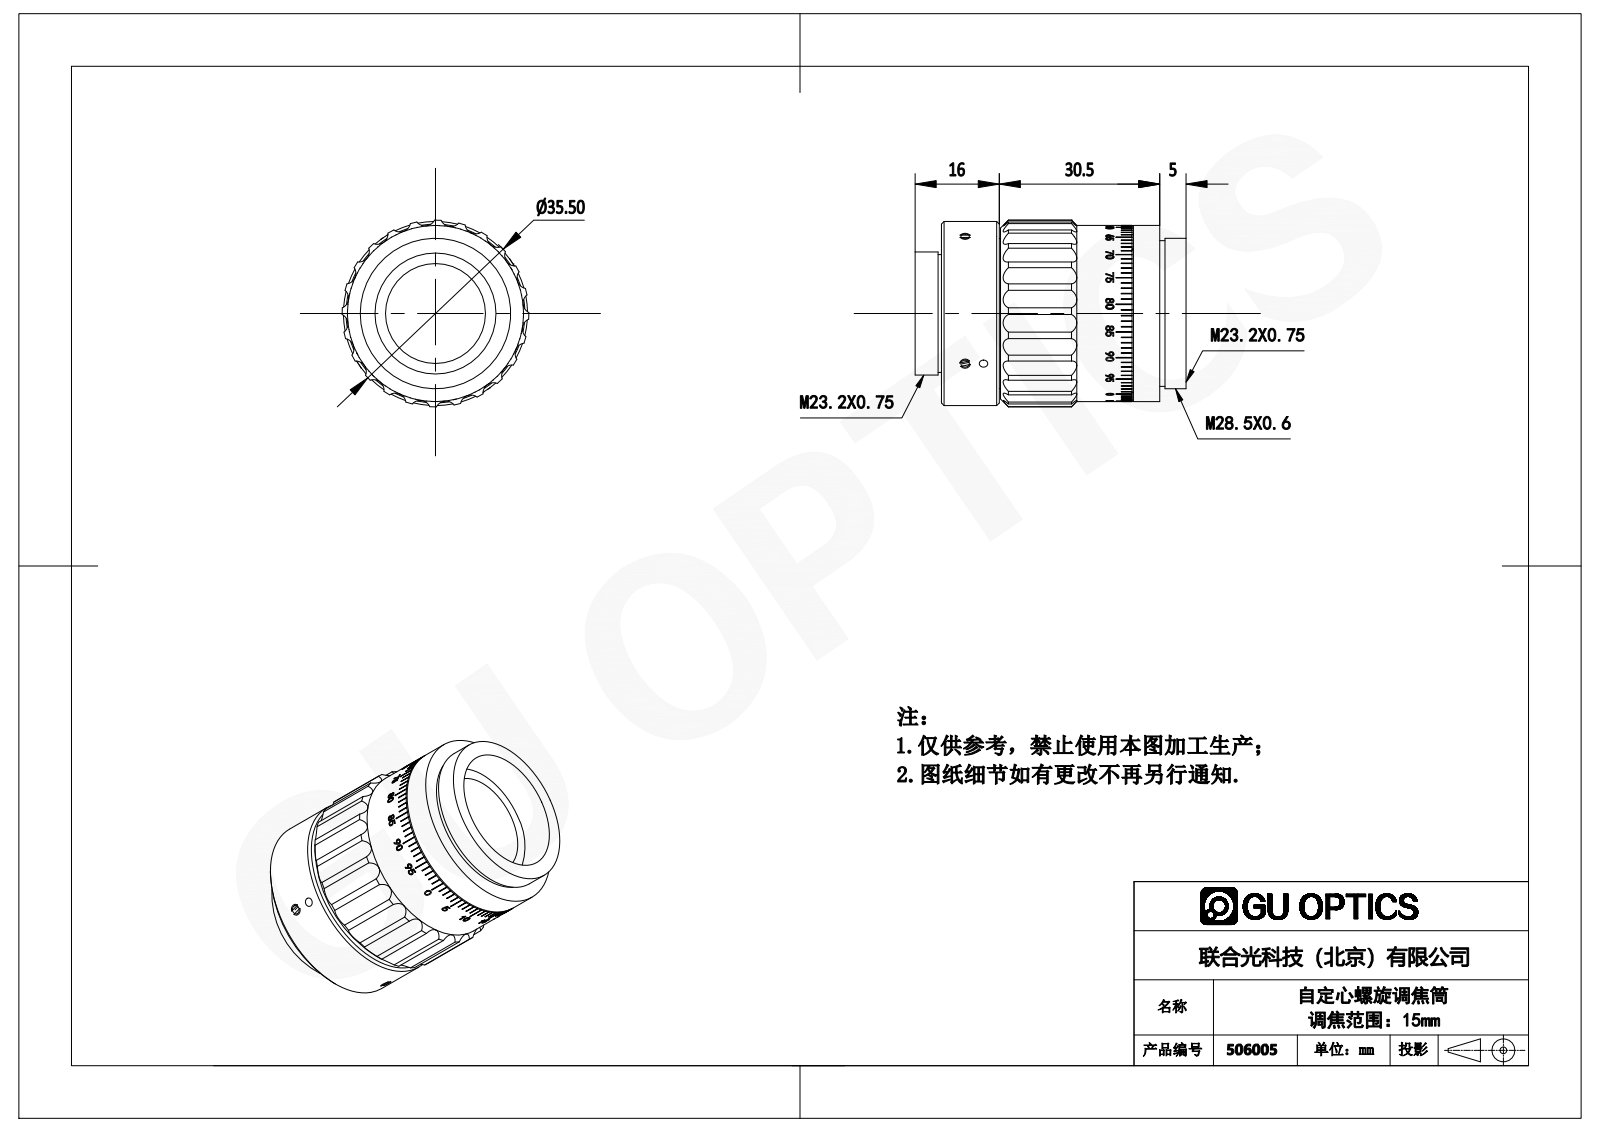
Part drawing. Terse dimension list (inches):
name: 506005
written by: SolidWorks 2016 (AUTOMOTIVE_DESIGN)
unit: in
bodies: 8 solids, 1555 faces (658 planar, 347 cylindrical, 550 other)
size: 2.028 × 1.398 × 1.398
volume: 1.625 in³; area: 37.89 in²
holes: 5× ⌀0.063, 2× ⌀0.083, 1× ⌀0.748, 1× ⌀0.906, 1× ⌀0.984, 1× ⌀1.004, 1× ⌀1.012, 1× ⌀1.13, 1× ⌀1.22, 1× ⌀1.26
bosses: 4× ⌀0.081, 4× ⌀0.079, 1× ⌀1.378, 1× ⌀1.319, 1× ⌀1.244, 1× ⌀1.201, 1× ⌀1.181, 1× ⌀1.126
rounds: 24× R0.079, 4× R0.502, 2× R0.492, 1× R0.587, 1× R0.659, 1× R0.699
face distances: 0.079, 0.197, 0.472, 0.551, 0.039, 1.152, 1.634, 0.481, 0.394, 1.358
hole spacings: 0.138
